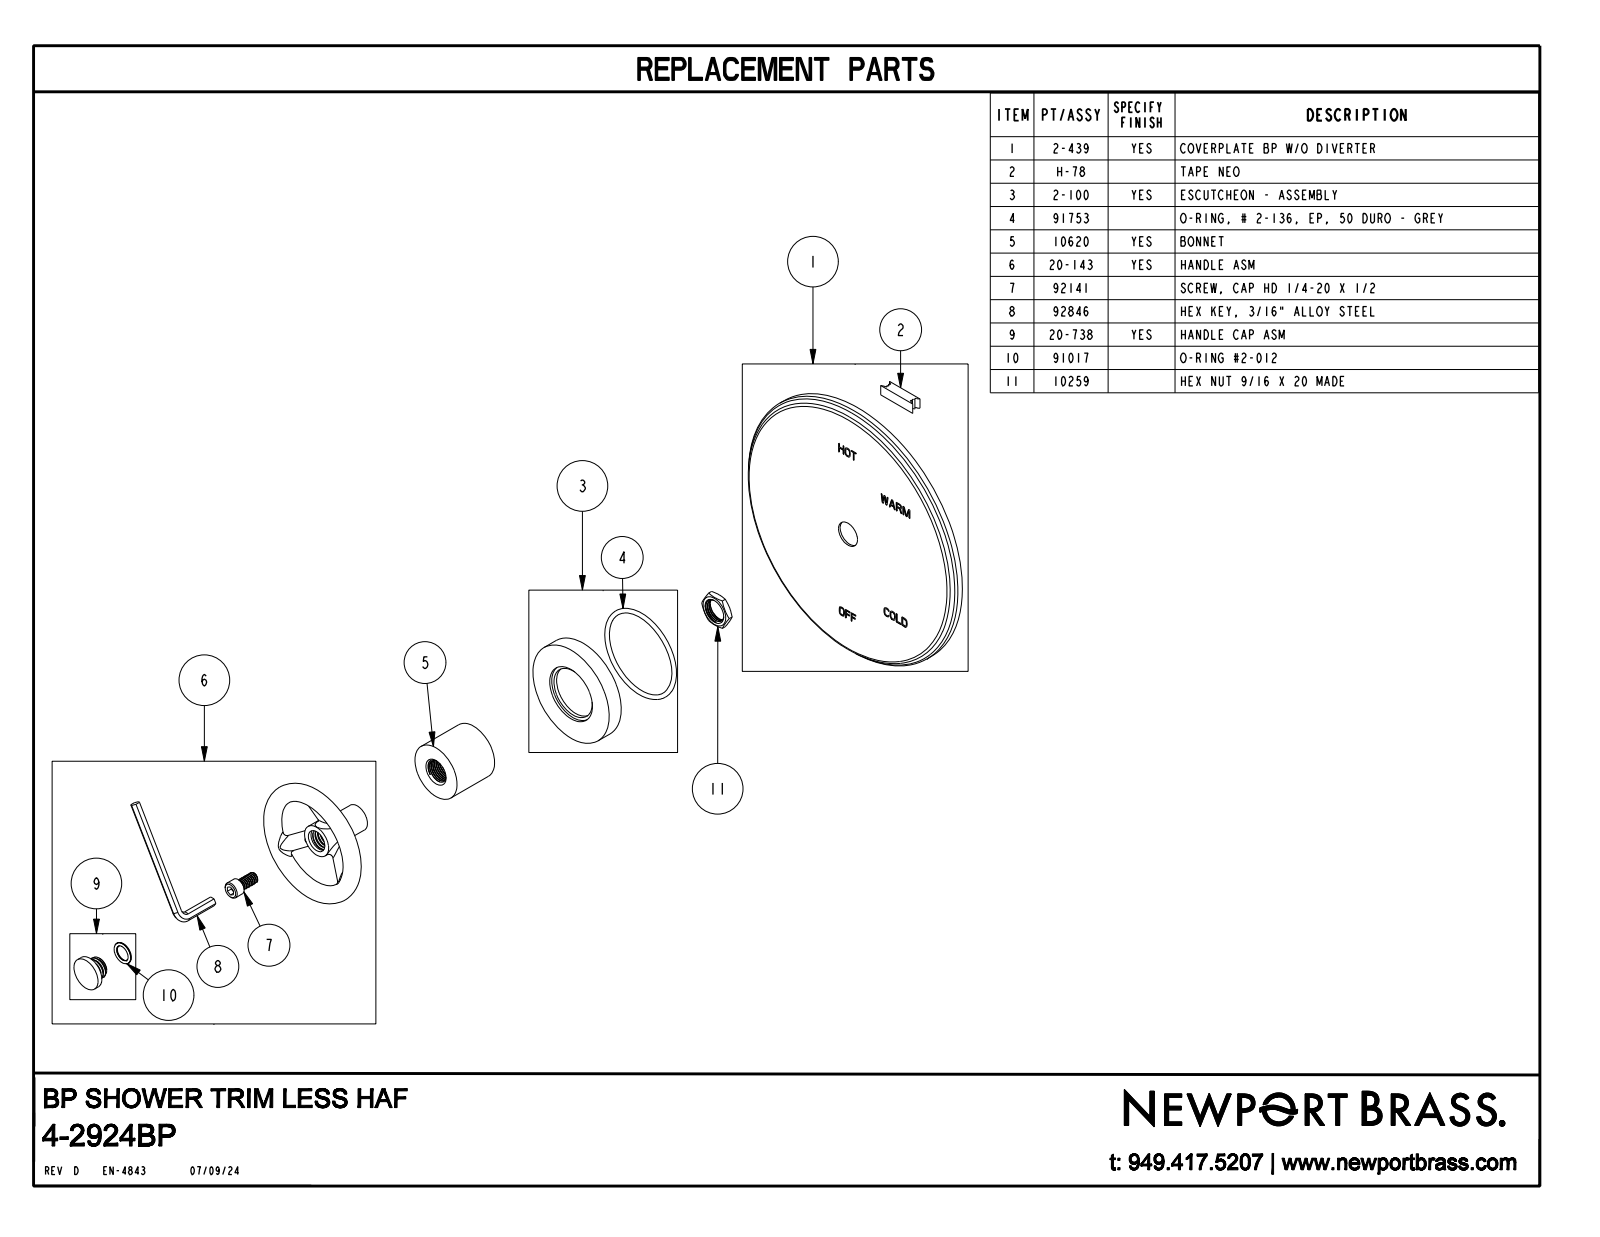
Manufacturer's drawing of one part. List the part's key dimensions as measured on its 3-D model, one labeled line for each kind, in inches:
Part name (STEP PRODUCT): 4-2924BP
STEP written by: CREO PARAMETRIC BY PTC INC, 2018400 (CONFIG_CONTROL_DESIGN)
Units: inches
Bodies: 1 solid, 380 faces (334 planar, 18 cylindrical, 28 other)
Overall size (bounding box): 6.5 × 6.5 × 3.416
Volume: 15.07 in³ · Surface area: 93.95 in²
Round bosses / shafts (diameter × count): ⌀0.35 ×3, ⌀6.5 ×1, ⌀2.375 ×1, ⌀1.313 ×1, ⌀0.75 ×1, ⌀0.63 ×1, ⌀0.4 ×1
Main face-to-face distances: 0.313, 0.688, 0.375, 1.796, 1.483, 1.108, 3.206, 2.893, 2.518, 1.41
